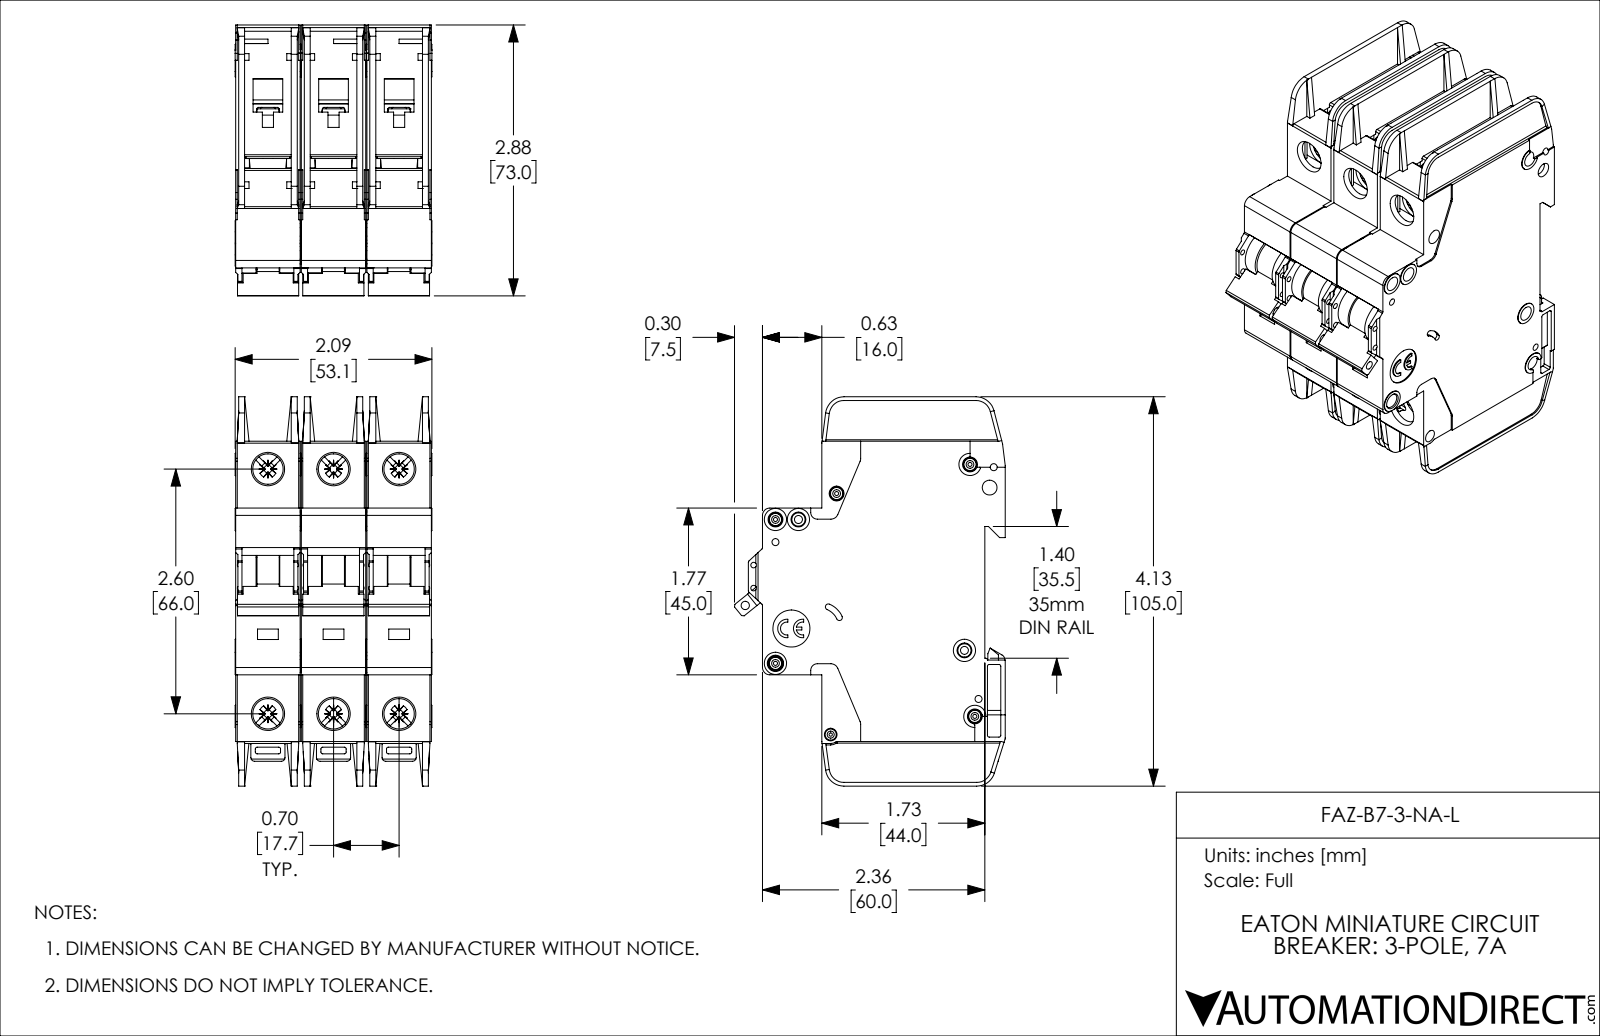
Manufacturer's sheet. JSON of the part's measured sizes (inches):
{"part_name": "FAZ-B7-3-NA-L", "step_written_by": "SolidWorks 2019 (AUTOMOTIVE_DESIGN)", "units": "inches", "bodies": {"solids": 3, "faces": 3381, "planar": 2013, "cylindrical": 1071, "other": 297}, "overall_size": [4.134, 2.876, 2.091], "volume_in3": 14.05, "surface_area_in2": 123, "round_holes": [[0.157, 8], [0.323, 6], [0.043, 5], [0.075, 4], [0.059, 2], [0.085, 2], [0.035, 1], [0.089, 1], [0.098, 1], [0.134, 1], [0.394, 1]], "round_bosses_or_shafts": [[0.13, 5], [0.236, 4], [0.118, 4], [0.098, 3]], "partial_cylinders_radius": [[0.02, 72], [0.016, 30], [0.039, 18], [0.043, 12], [0.079, 12], [0.008, 6], [0.01, 6], [0.028, 6]], "face_to_face_distances": [0.697, 0.047, 1.394, 0.685, 0.591, 1.382, 0.744, 0.65, 0.106, 0.094], "hole_center_spacings": [0.697, 2.69, 2.598, 0.244, 0.537, 0.87, 1.394, 2.948]}
